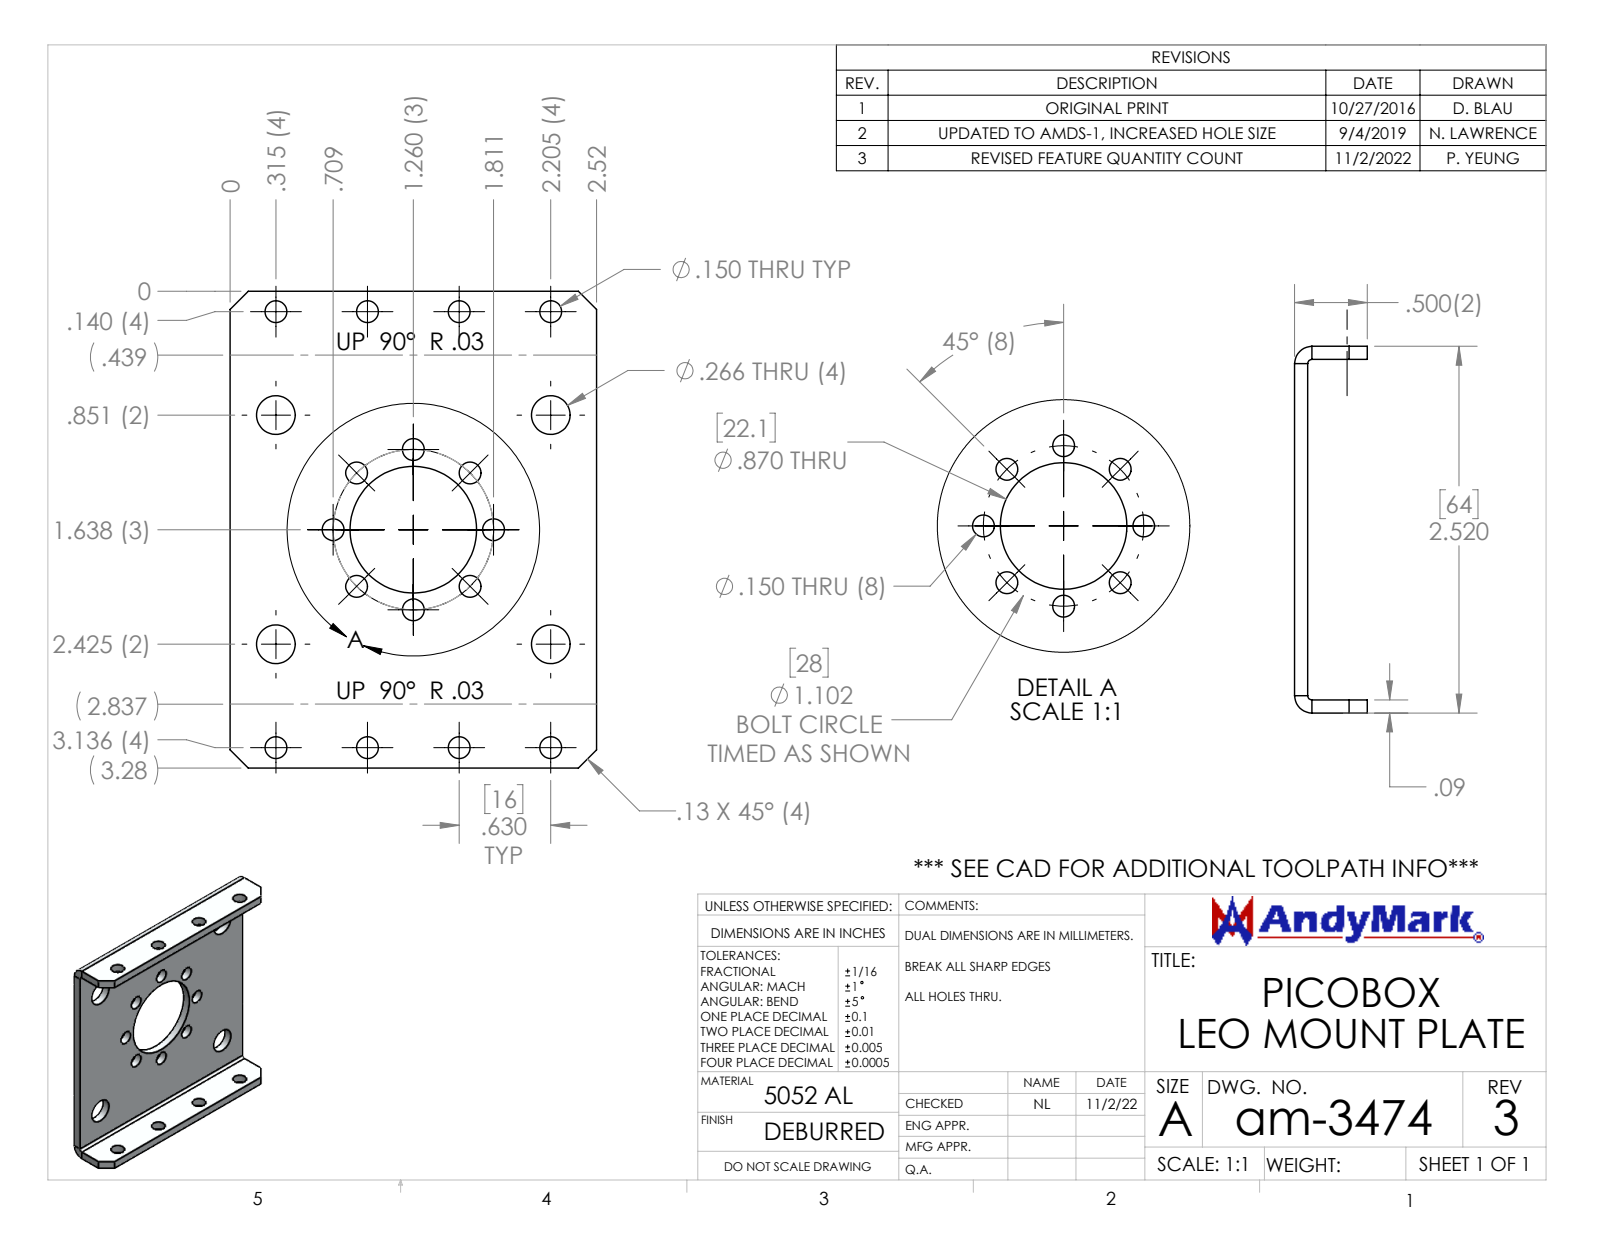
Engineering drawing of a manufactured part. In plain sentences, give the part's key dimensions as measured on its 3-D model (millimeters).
The part is named "am-3474 PicoBox LEO Plate". Its 3-D file was written by "SolidWorks 2022 (CONFIG_CONTROL_DESIGN)". It is 1 solid with 68 faces: 22 planar, 46 cylindrical and 0 other. Overall it measures 64 by 64 by 12.7 millimeters. Its volume is 10 500 cubic millimeters and its surface area 10 640 square millimeters. Round holes: 12 of diameter 3.8, 4 of diameter 6.8, 1 of diameter 22.1. Partial cylindrical surfaces (rounded edges, fillets, slot ends): 2 of radius 0.7, 2 of radius 3. The main face-to-face distances are 2.3, 61.7, 64, 59.4, 12.7, 10.4. The hole center spacings are 10.7, 14, 19.8, 25.9, 17.3, 22.4, 24.7, 28.
